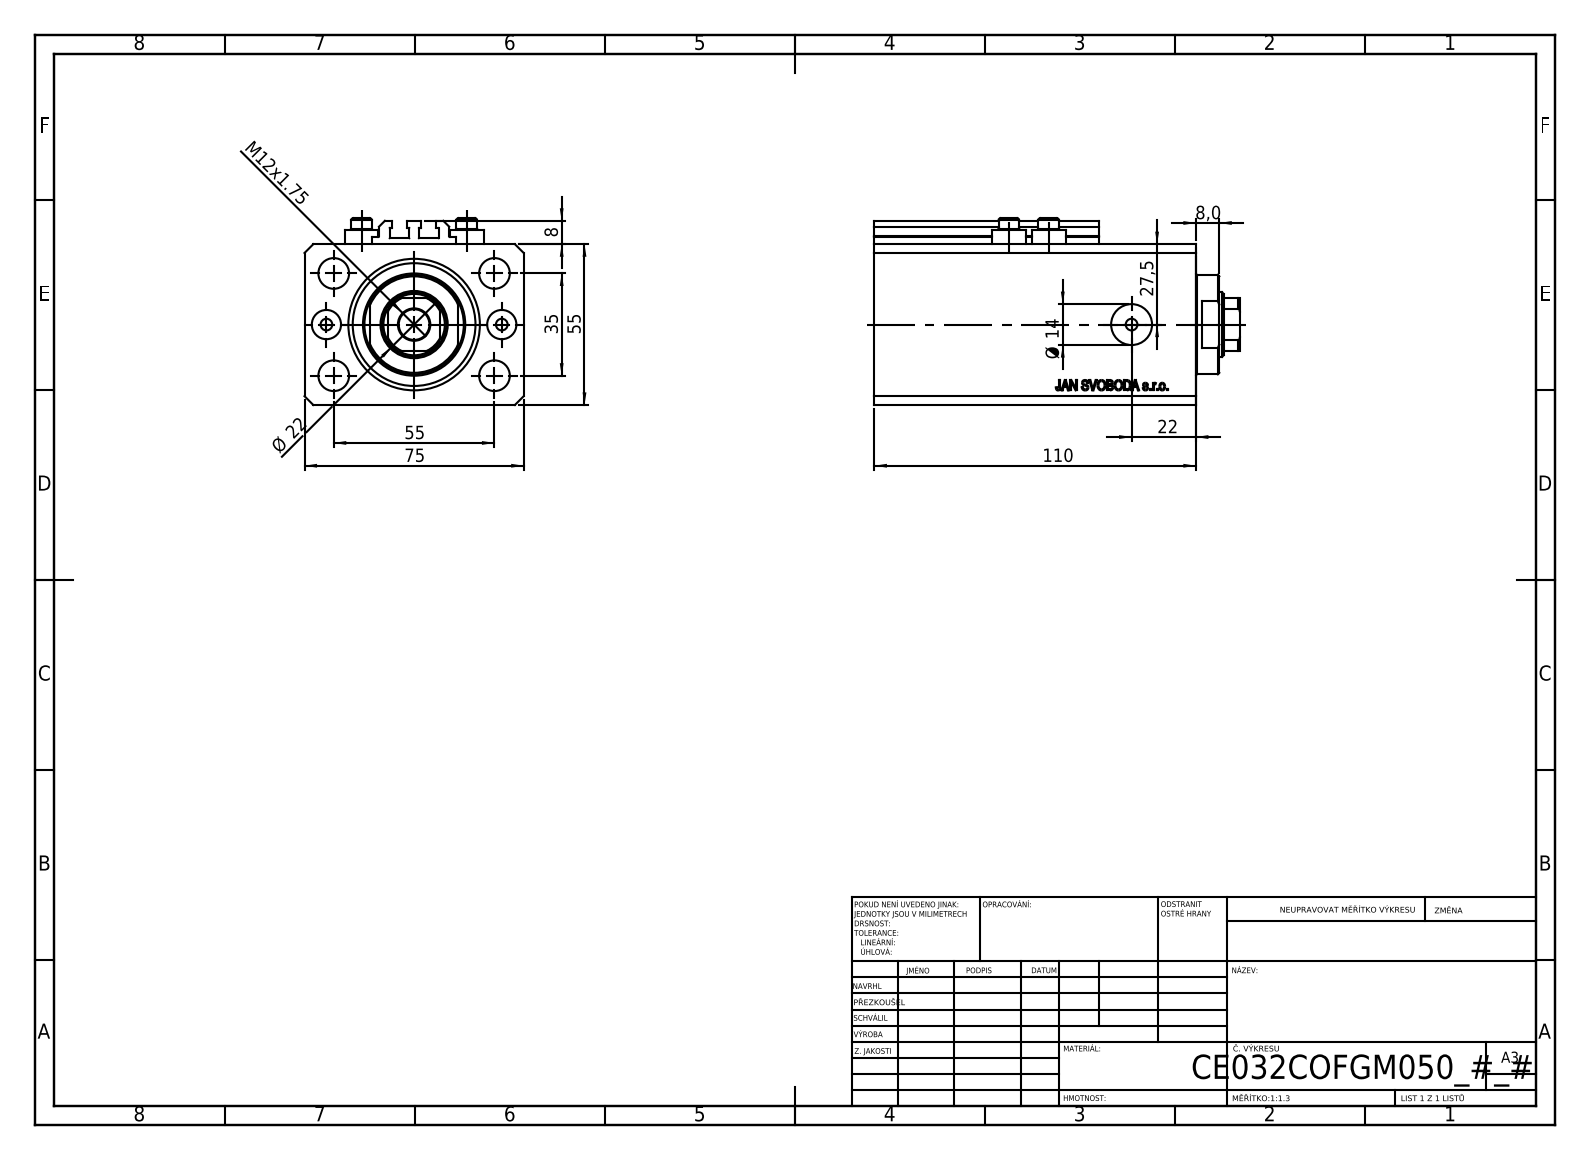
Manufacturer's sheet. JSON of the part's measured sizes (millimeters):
{"part_name": "ALLEN BOLT V250CE; V250CE_VC_C; V250CE_C_Body; V250CE_C_VCP", "step_written_by": "SolidWorks 2019 (CONFIG_CONTROL_DESIGN)", "units": "millimeters", "bodies": {"solids": 8, "faces": 1034, "planar": 504, "cylindrical": 86, "other": 444}, "overall_size": [125, 75, 64], "volume_mm3": 408931, "surface_area_mm2": 91117, "round_holes": [[4, 8], [10.5, 5], [10, 2], [14, 2], [22, 1], [32, 1], [45, 1]], "round_bosses_or_shafts": [[11.6, 4], [7, 4], [34, 1]], "partial_cylinders_radius": [[0.2, 10], [10.5, 1]], "face_to_face_distances": [55, 75, 110, 15, 95, 9.9, 85.1, 100.1, 3, 8], "hole_center_spacings": [17.68, 32.6, 60.1, 13.6, 30, 35, 36, 38.48]}
